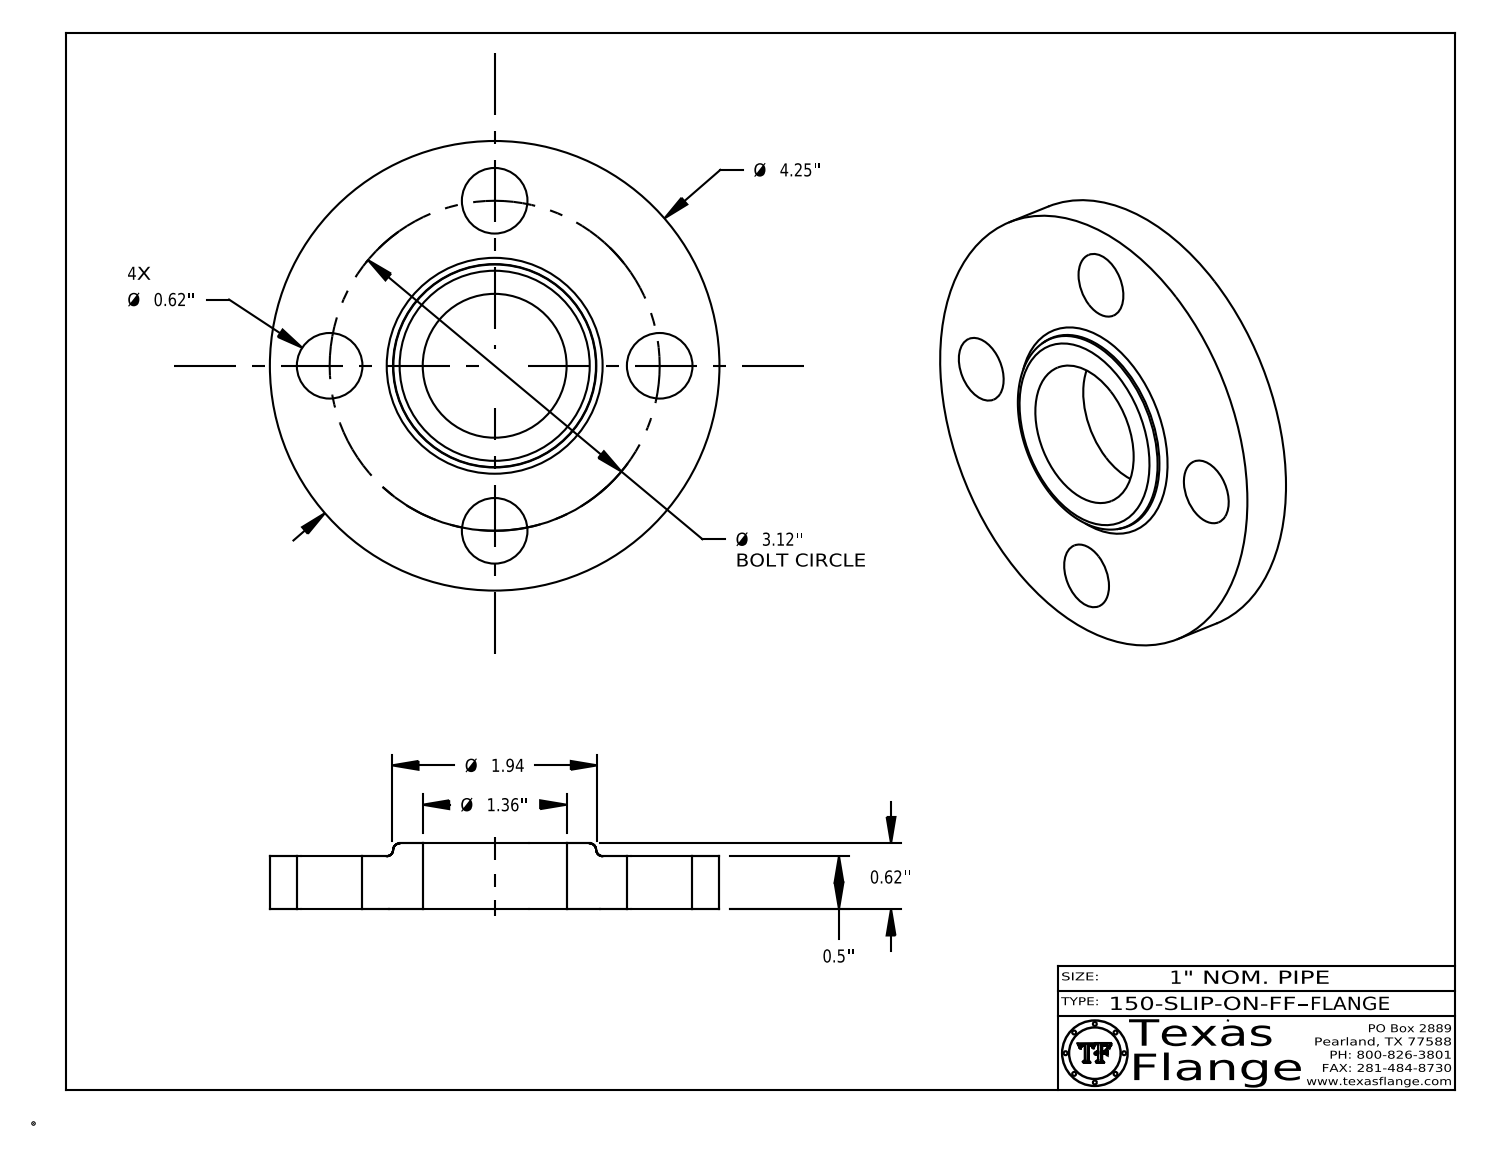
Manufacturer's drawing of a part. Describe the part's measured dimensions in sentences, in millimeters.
The part is named "150-SLIP-ON-FF". Its 3-D file was written by "CATIA V5 STEP AP214 (AUTOMOTIVE_DESIGN)". It is 1 solid with 407 faces: 369 planar, 32 cylindrical and 6 other. Overall it measures 108 by 108 by 15.7 millimeters. Its volume is 97 260 cubic millimeters and its surface area 23 720 square millimeters. Round holes: 4 of diameter 15.7, 1 of diameter 12.6, 1 of diameter 34.5. Round bosses or shafts: 8 of diameter 0.8, 1 of diameter 108, 1 of diameter 9.9. The main face-to-face distances are 12.7, 15.7, 3, 12.3, 0.4, 3.4, 3.8, 3.7, 0.7, 3.1. The hole center spacings are 39.6, 56, 30.3, 73.2, 79.2, 39.6.
